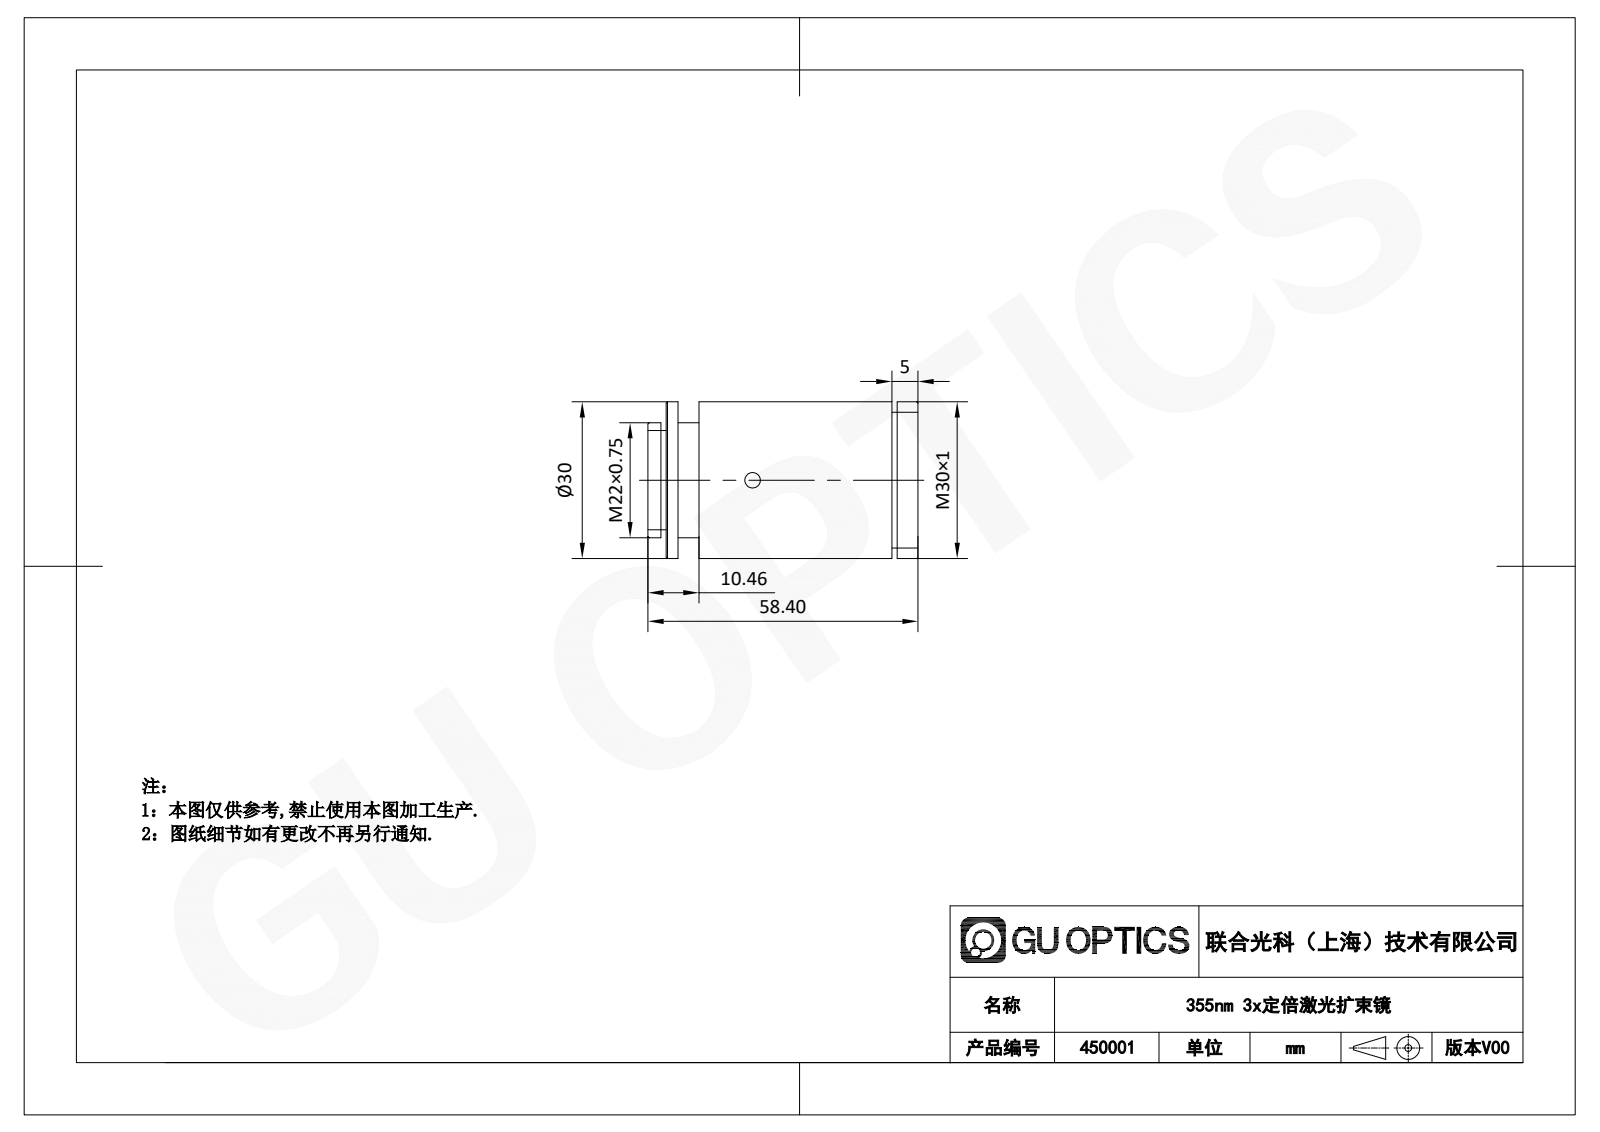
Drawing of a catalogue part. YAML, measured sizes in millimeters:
part_name: "450001"
step_written_by: "SolidWorks 2020 (AUTOMOTIVE_DESIGN)"
units: millimeters
bodies: {solids: 1, faces: 43, planar: 11, cylindrical: 22, other: 10}
overall_size: [58.4, 30, 30]
volume: 31391
surface_area: 10499
round_holes:
  - {diameter: 8, count: 1}
  - {diameter: 18, count: 1}
round_bosses_or_shafts:
  - {diameter: 30, count: 1}
  - {diameter: 26, count: 1}
  - {diameter: 22, count: 1}
  - {diameter: 19, count: 1}
face_to_face_distances: [4, 47.94, 50.9, 54.9, 2.96, 51.94, 6.96, 43.94, 3.5, 6.46]
